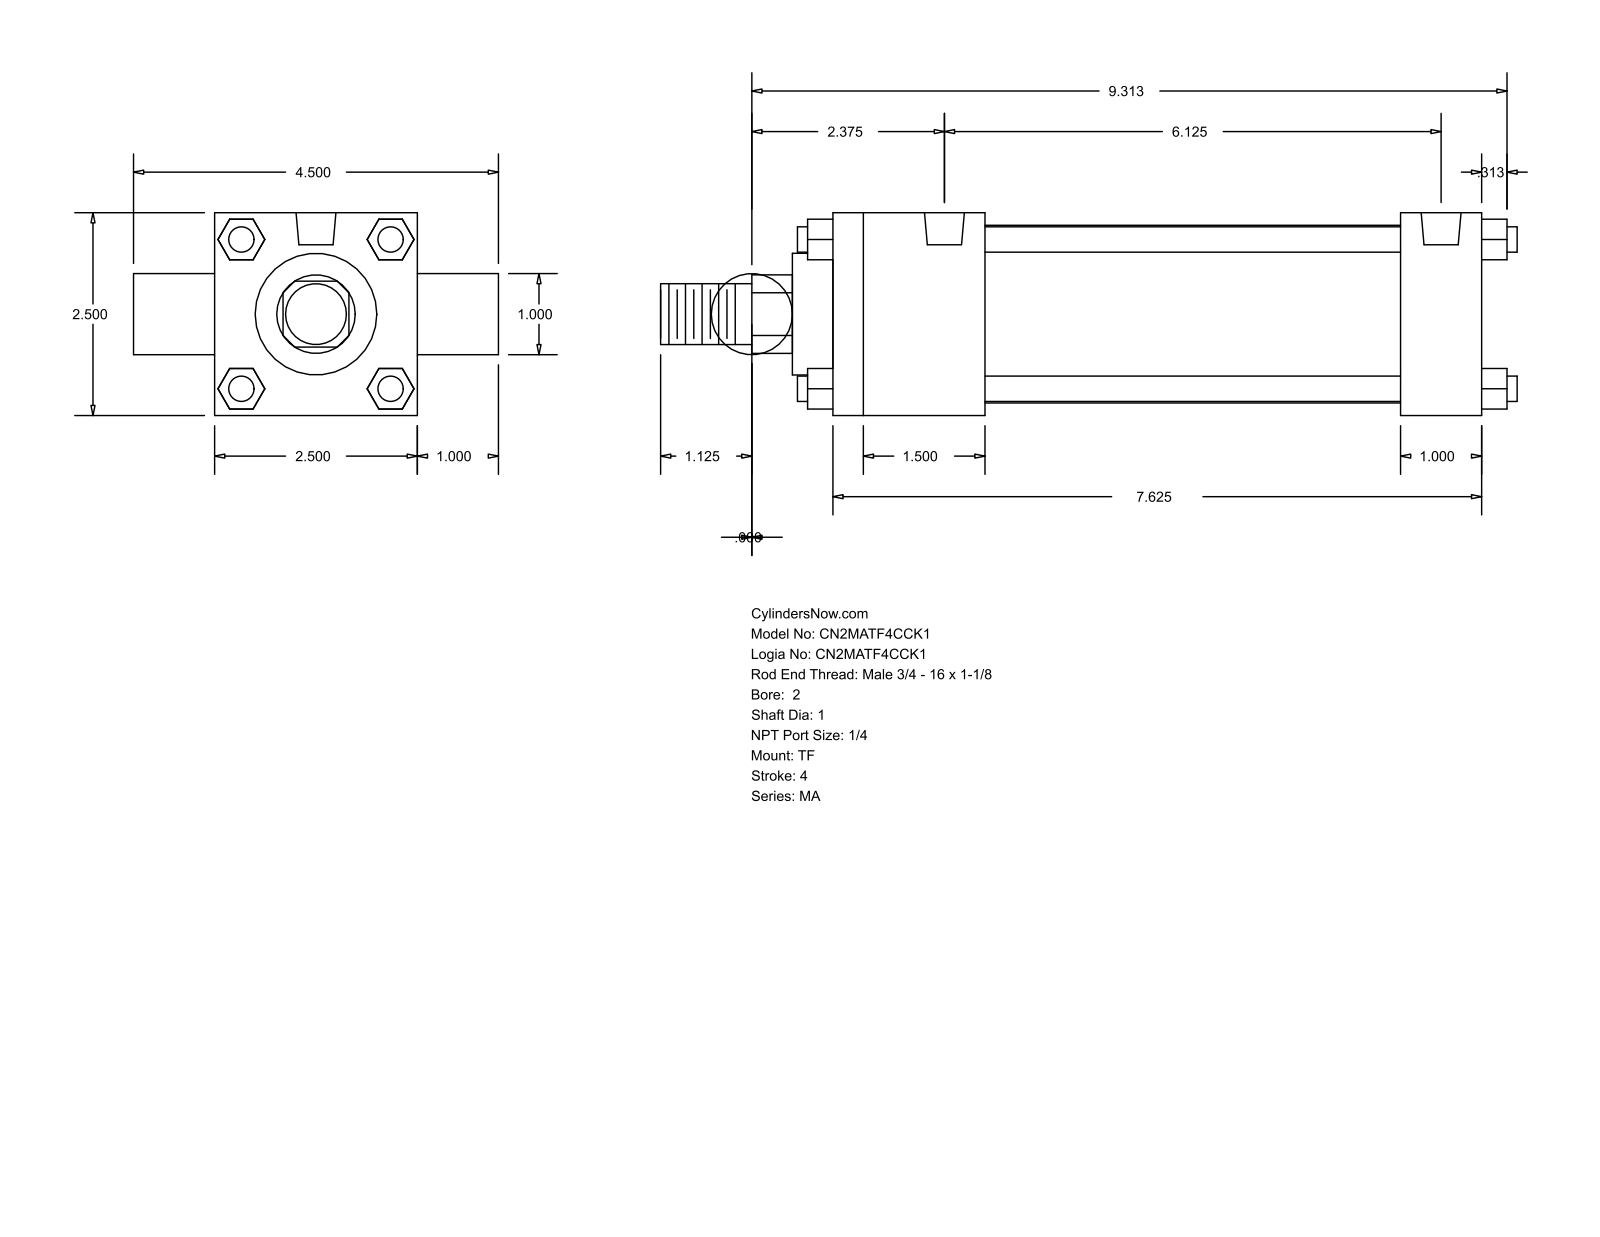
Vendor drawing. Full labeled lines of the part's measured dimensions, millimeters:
Part name (STEP PRODUCT): MA_TF__0200_1
STEP written by: GSSL Pune (CONFIG_CONTROL_DESIGN)
Units: millimetres
Bodies: 0 solids, 120 faces (92 planar, 28 cylindrical, 0 other)
Overall size (bounding box): 268.29 × 114.3 × 63.5
Round holes (diameter × count): ⌀7.94 ×3, ⌀12.49 ×2
Round bosses / shafts (diameter × count): ⌀7.94 ×4, ⌀25.4 ×2, ⌀55.63 ×1, ⌀38.1 ×1, ⌀19.05 ×1
Partial cylindrical surfaces — rounded edges, fillets, slot ends (radius × count): R12.29 ×1
Main face-to-face distances: 63.5, 25.4, 203.2, 12.7, 47.63, 177.8, 130.17, 155.57, 88.9, 40.47
Hole centre spacings: 155.57
